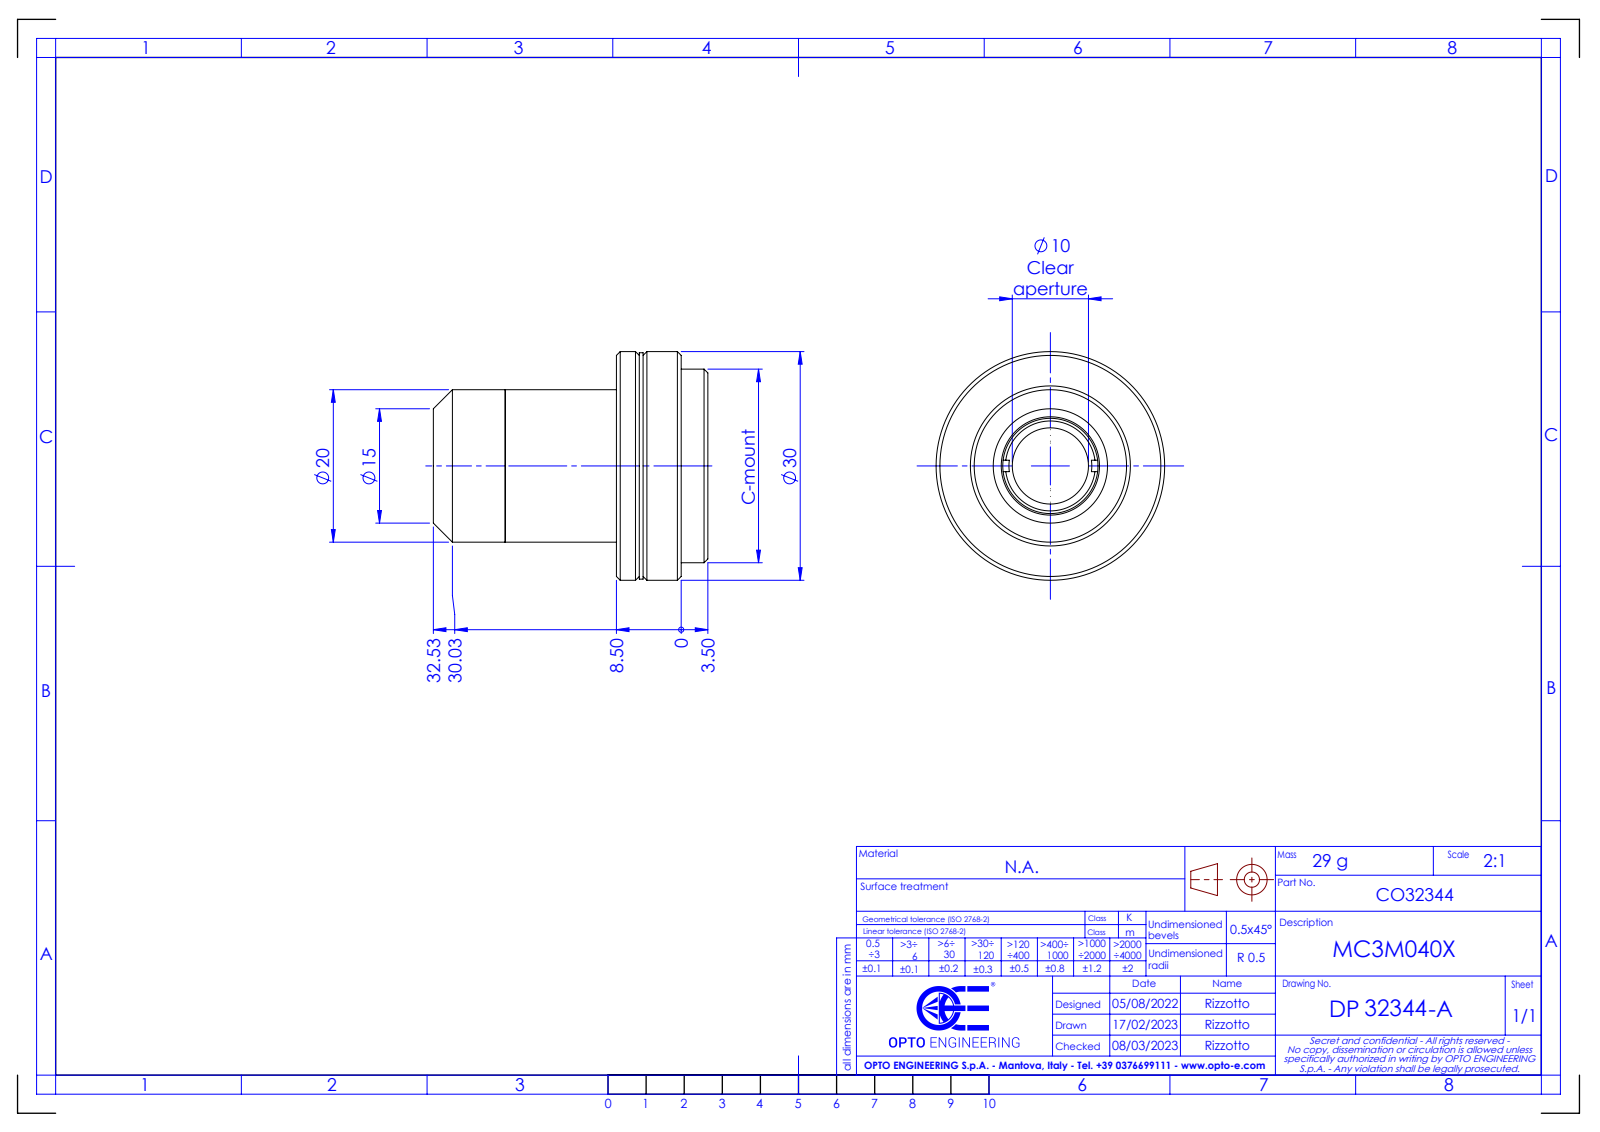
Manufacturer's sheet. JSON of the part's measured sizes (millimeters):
{"part_name": "DP32344-A_MC3M040X", "step_written_by": "SolidWorks 2021 (CONFIG_CONTROL_DESIGN)", "units": "millimeters", "bodies": {"solids": 0, "faces": 66, "planar": 18, "cylindrical": 22, "other": 26}, "overall_size": [36.03, 30, 30], "round_holes": [[10, 1], [12.5, 1], [15.5, 1], [18, 1]], "round_bosses_or_shafts": [[30, 1], [29.7, 1], [25.4, 1], [20, 1]], "face_to_face_distances": [8.5, 3.5, 5, 3, 0.5, 5.5, 12, 9, 14.6, 17.6]}
